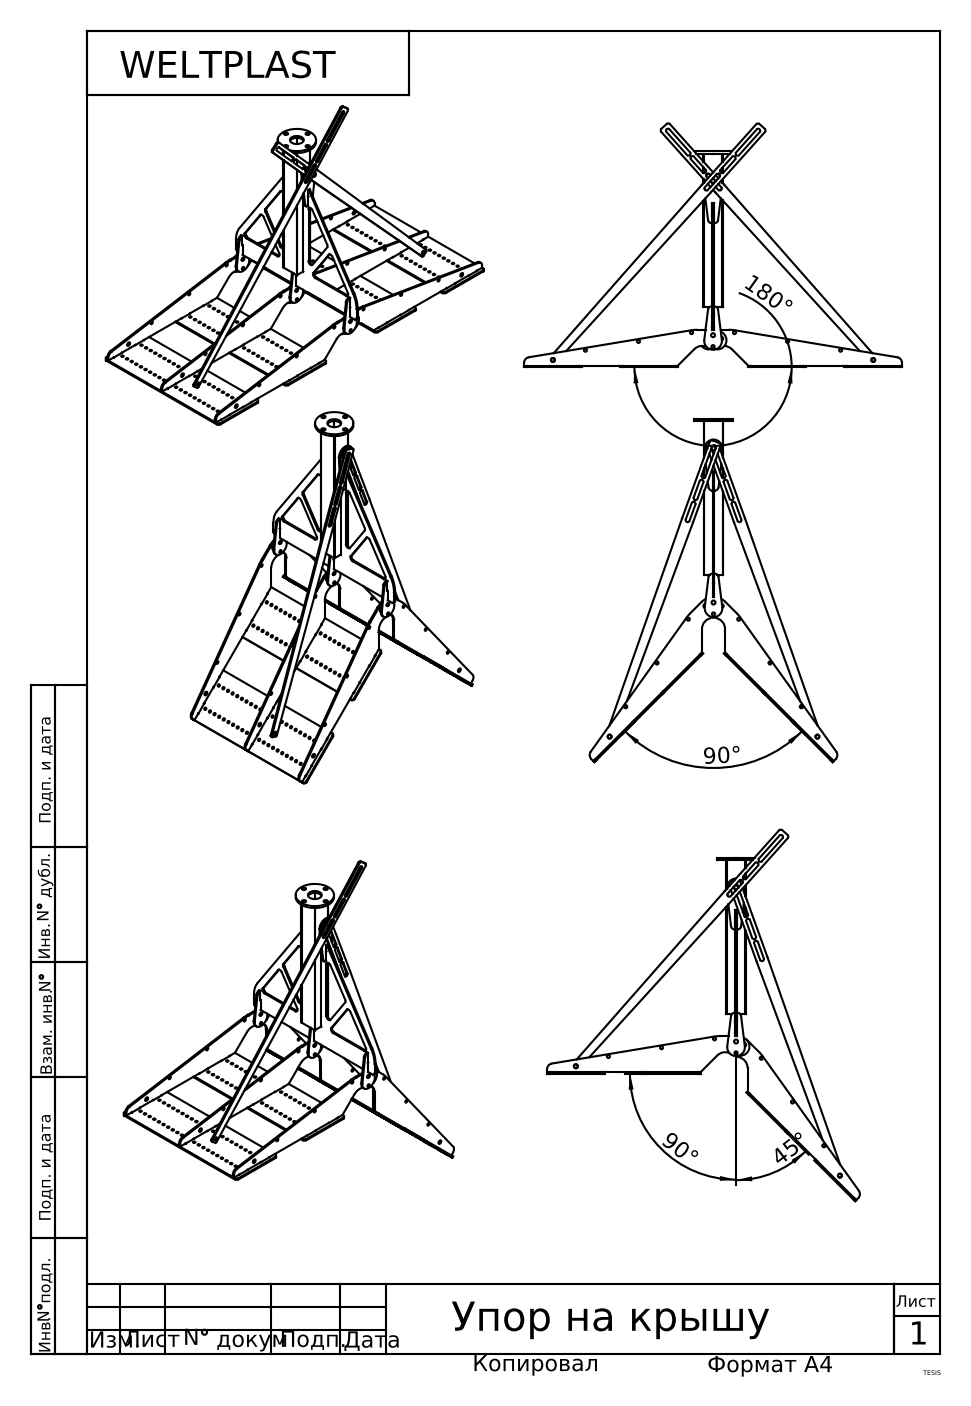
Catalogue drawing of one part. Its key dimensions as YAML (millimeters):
part_name: "Тяга; Сборка Лапы; Стрингер; Подошва (+7 more)"
step_written_by: "SolidWorks 2017 (AUTOMOTIVE_DESIGN)"
units: millimeters
bodies: {solids: 19, faces: 1032, planar: 388, cylindrical: 644, other: 0}
overall_size: [807.73, 807.38, 444]
volume: 2266000
surface_area: 1317000
round_holes:
  - {diameter: 6.4, count: 176}
  - {diameter: 8, count: 6}
  - {diameter: 10.4, count: 4}
  - {diameter: 11, count: 4}
  - {diameter: 10, count: 2}
  - {diameter: 8.4, count: 1}
  - {diameter: 36, count: 1}
round_bosses_or_shafts:
  - {diameter: 100, count: 1}
partial_cylinders:
  - {radius: 2, count: 16}
  - {radius: 5.2, count: 16}
  - {radius: 7, count: 16}
  - {radius: 8, count: 16}
  - {radius: 1, count: 5}
  - {radius: 4, count: 4}
  - {radius: 6, count: 4}
  - {radius: 10, count: 4}
face_to_face_distances: [4, 198, 202, 194, 8, 396, 48, 254, 56, 142]
hole_center_spacings: [34, 72.03, 86.61, 68, 17, 110.11, 77.82, 102]
